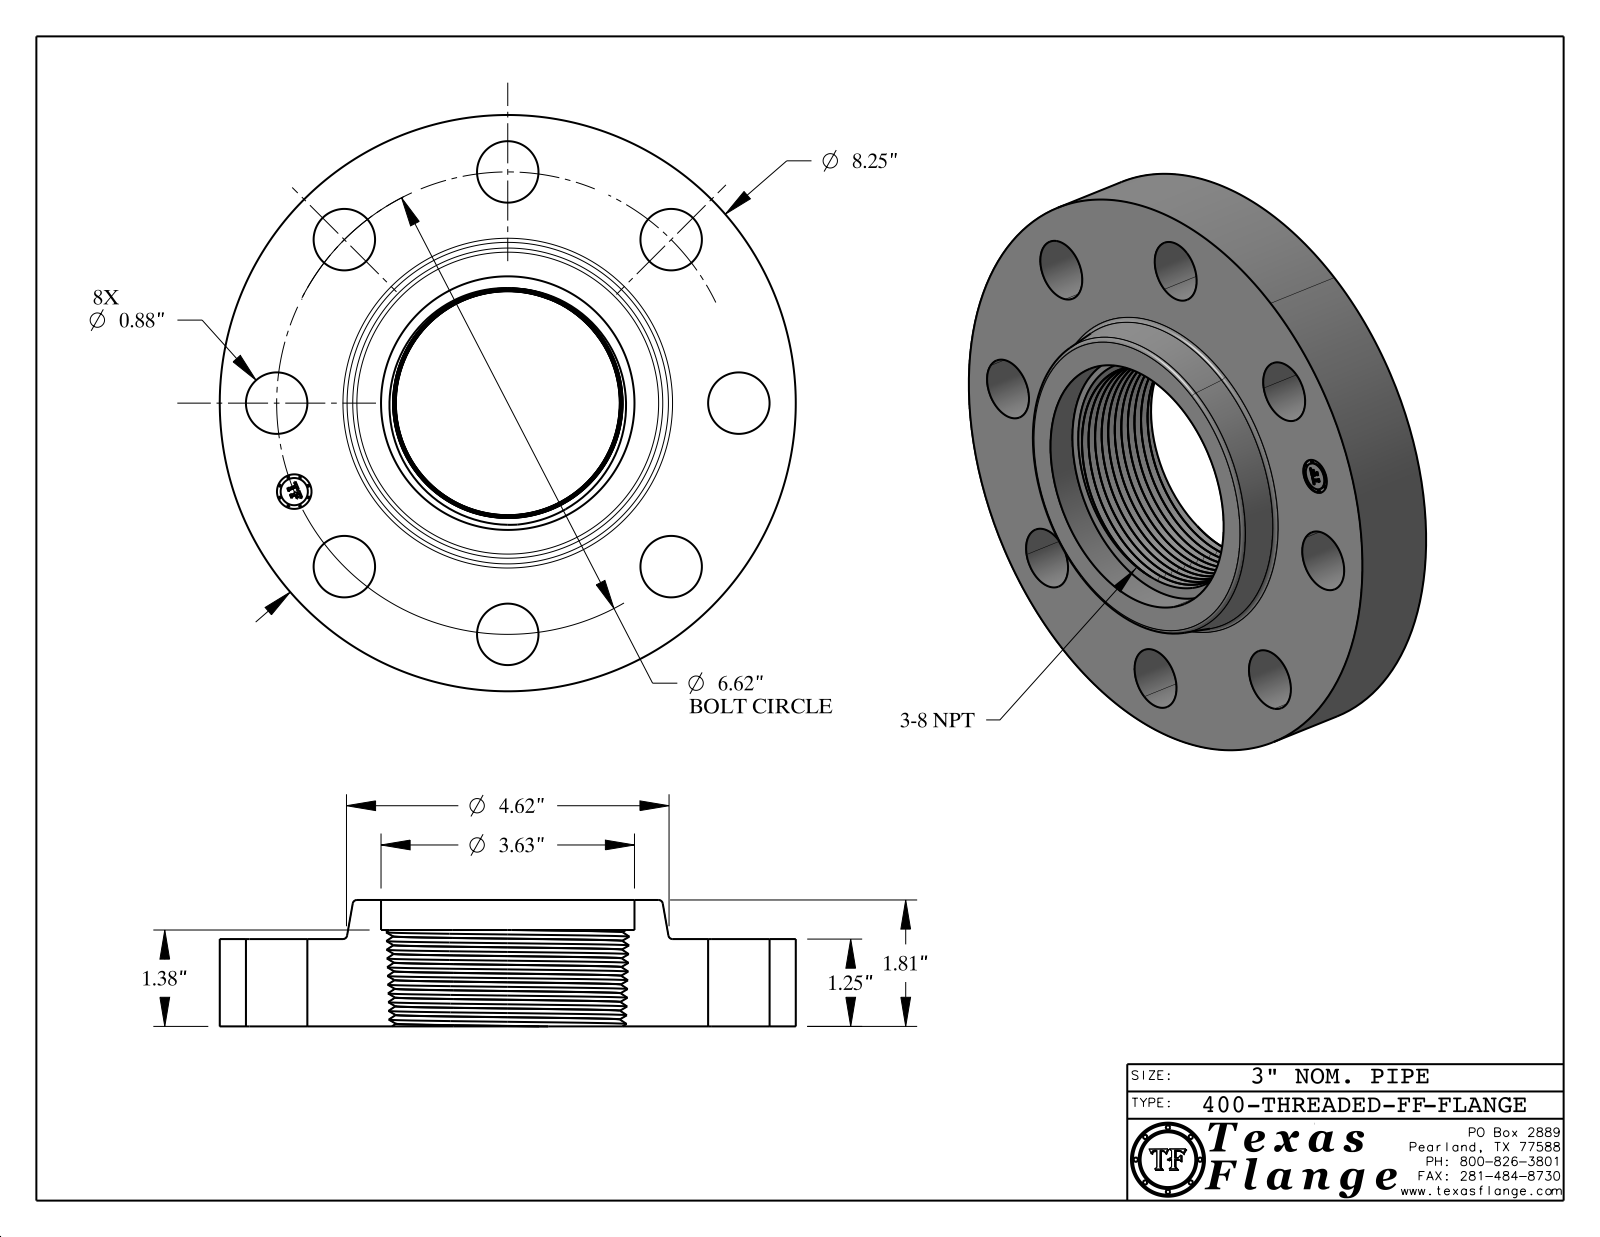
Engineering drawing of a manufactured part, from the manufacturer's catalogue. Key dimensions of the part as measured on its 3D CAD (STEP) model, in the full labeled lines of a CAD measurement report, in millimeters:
Part name (STEP PRODUCT): 400-THREADED-FF
STEP written by: CATIA V5 STEP AP214 (AUTOMOTIVE_DESIGN)
Units: millimetres
Bodies: 1 solid, 533 faces (369 planar, 40 cylindrical, 124 other)
Overall size (bounding box): 209.6 × 209.6 × 46
Volume: 871 000 mm³ · Surface area: 114 800 mm²
Round holes (diameter × count): ⌀22.4 ×8, ⌀12.6 ×1, ⌀92.2 ×1
Round bosses / shafts (diameter × count): ⌀0.8 ×8, ⌀209.6 ×1, ⌀9.9 ×1
Main face-to-face distances: 31.8, 46, 14.2, 35.1, 3.3, 10.9, 3.7, 0.4, 31.4, 14.6
Hole centre spacings: 84.1, 64.3, 155.3, 118.9, 118.9, 32.8, 93.4, 164.9
